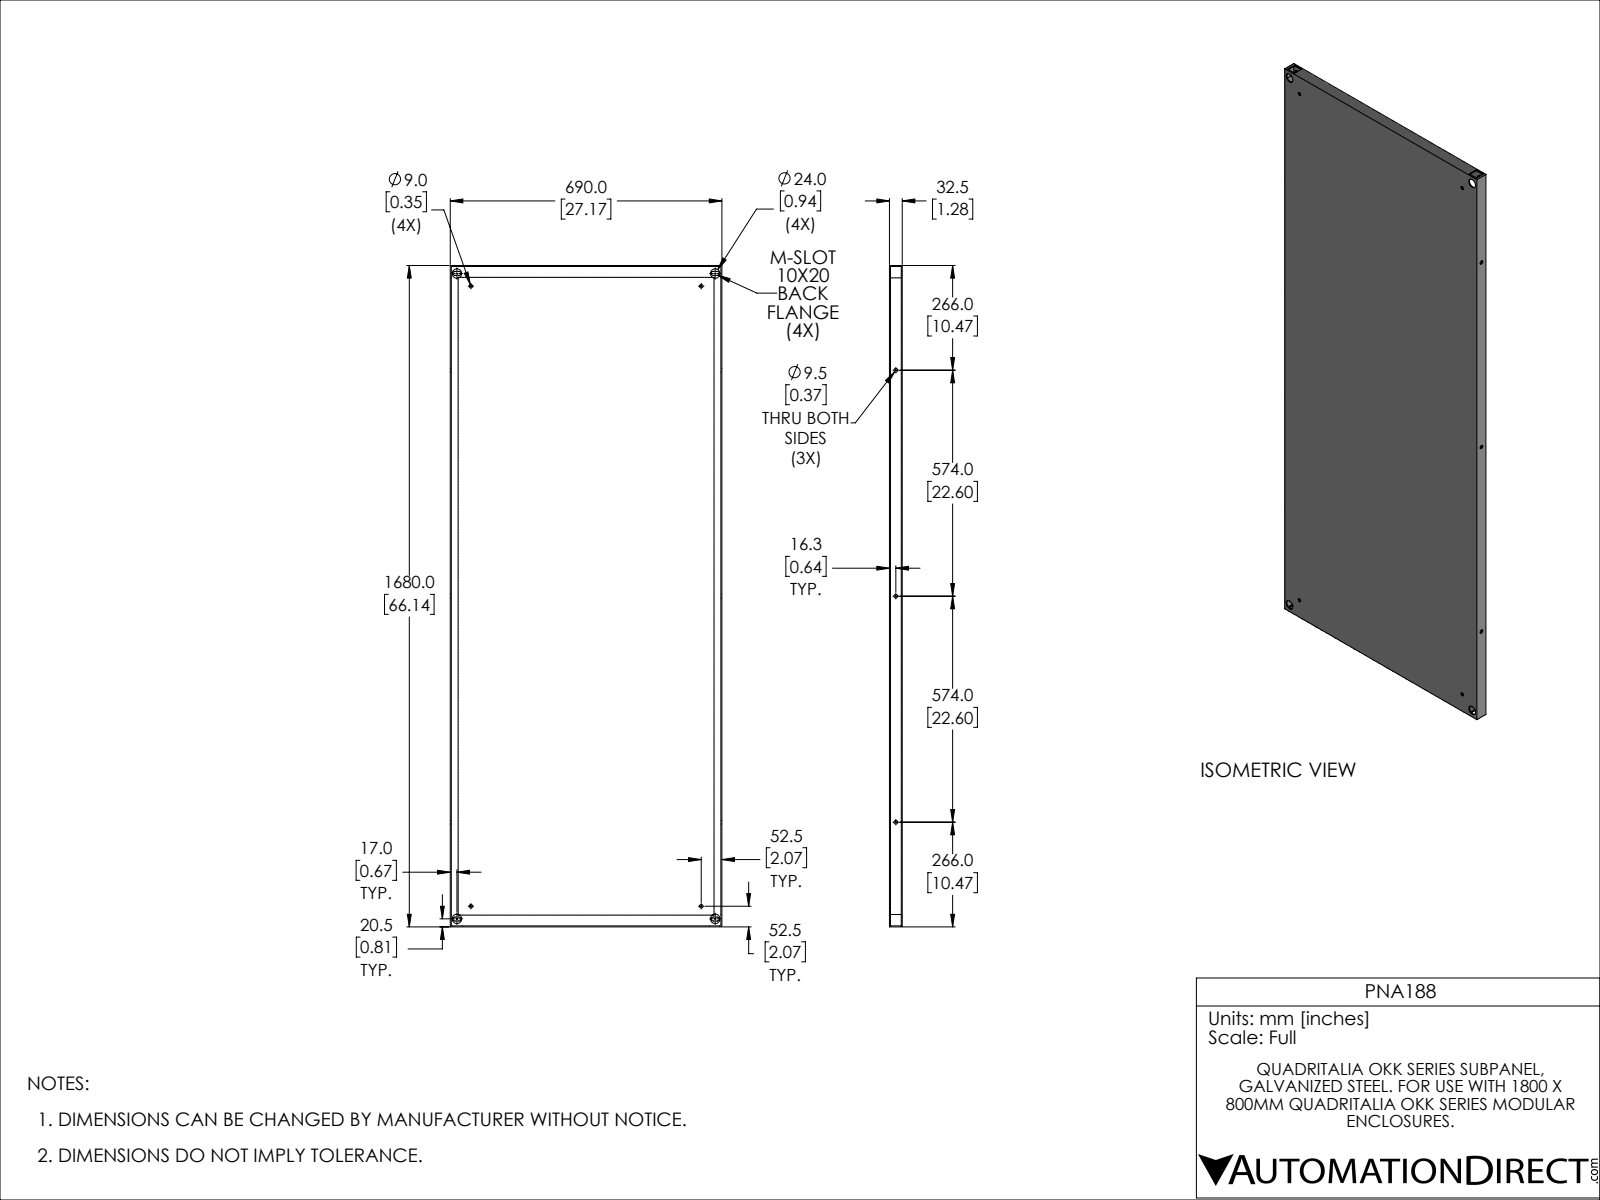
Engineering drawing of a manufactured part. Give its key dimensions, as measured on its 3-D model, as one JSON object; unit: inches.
{"part_name": "PNA188", "step_written_by": "SolidWorks 2021 (CONFIG_CONTROL_DESIGN)", "units": "inches", "bodies": {"solids": 1, "faces": 70, "planar": 48, "cylindrical": 22, "other": 0}, "overall_size": [66.142, 27.165, 1.28], "volume_in3": 212, "surface_area_in2": 4331, "round_holes": [[0.354, 4], [0.945, 4], [0.374, 3]], "partial_cylinders_radius": [[0.197, 8]], "face_to_face_distances": [0.098, 1.181, 1.28, 1.083, 27.067, 27.165, 26.969, 66.043, 66.142, 65.945], "hole_center_spacings": [1.881, 24.461, 63.283, 67.82, 22.598, 23.031, 25.827, 62.008]}
